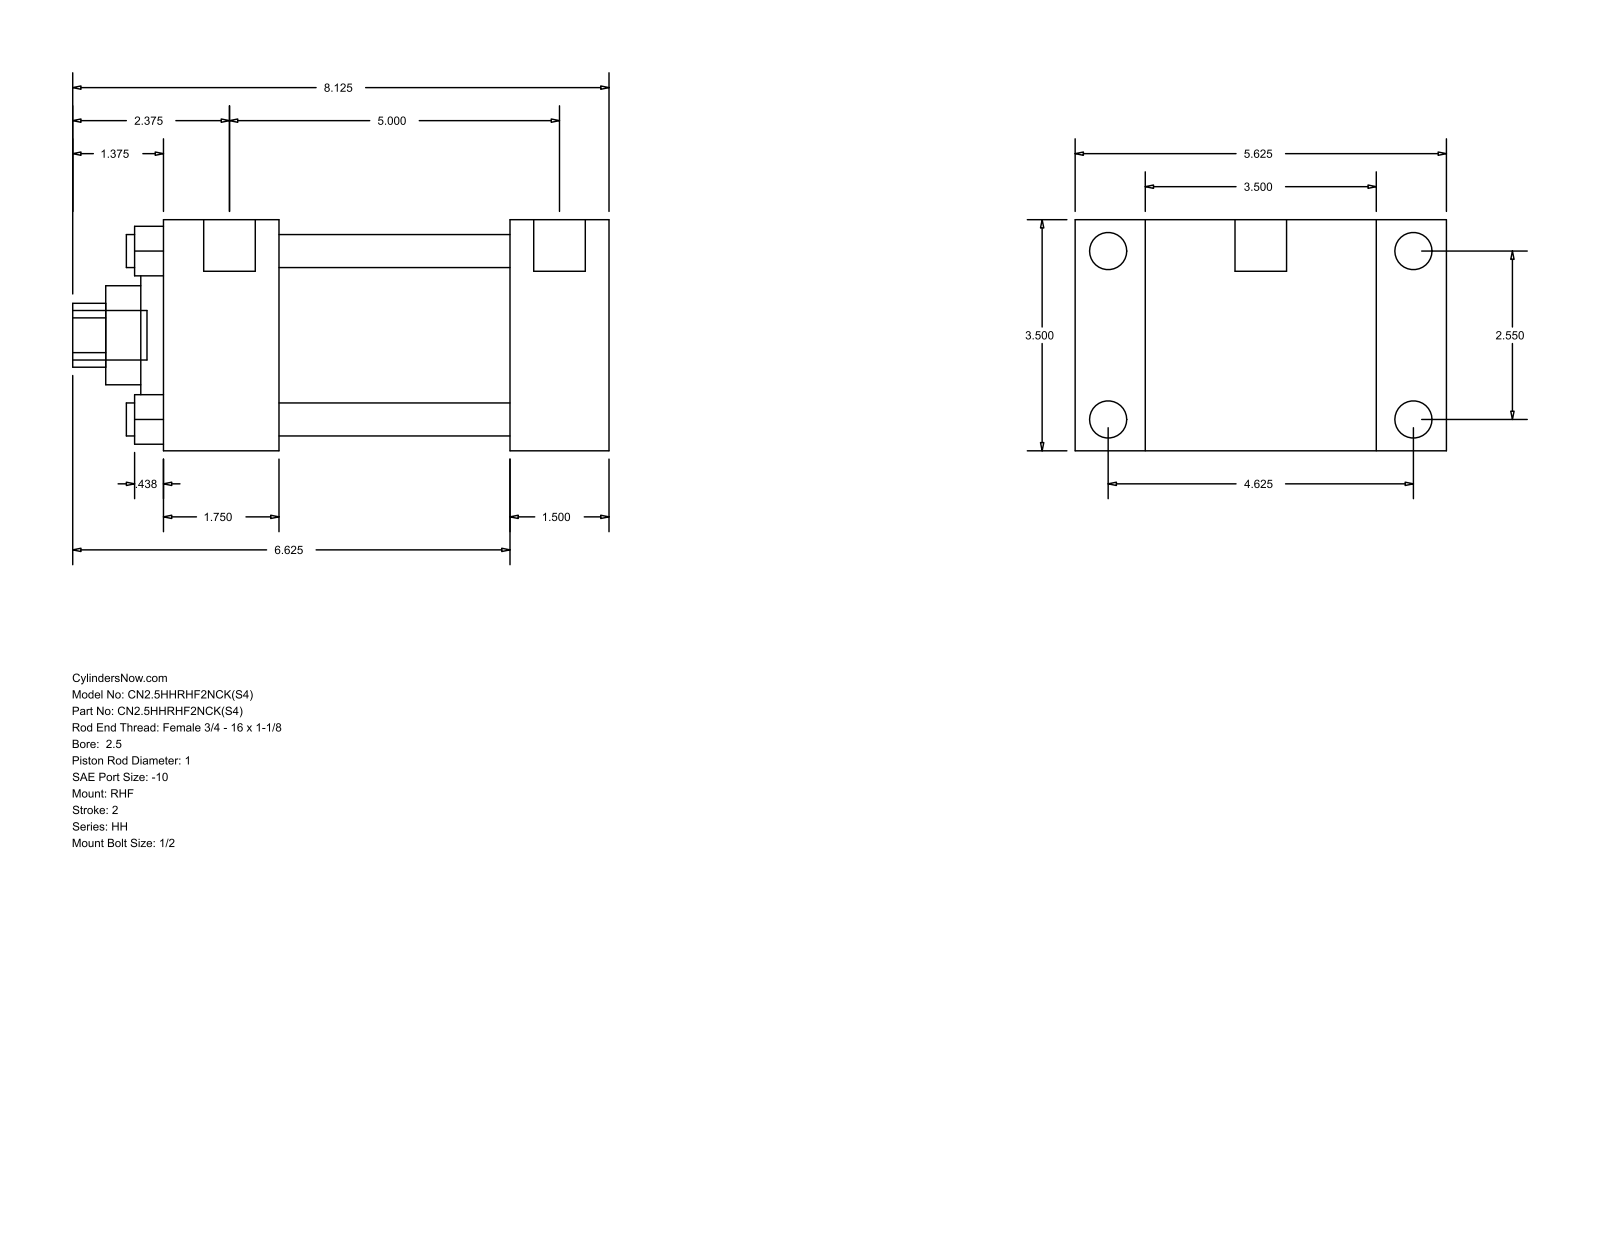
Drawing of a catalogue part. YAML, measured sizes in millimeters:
part_name: "HH_RHF__0250_1"
step_written_by: "GSSL Pune (CONFIG_CONTROL_DESIGN)"
units: millimeters
bodies: {solids: 0, faces: 90, planar: 61, cylindrical: 29, other: 0}
overall_size: [206.38, 142.88, 88.9]
round_holes:
  - {diameter: 12.7, count: 4}
  - {diameter: 25.4, count: 1}
  - {diameter: 38.1, count: 1}
  - {diameter: 60.33, count: 1}
  - {diameter: 73.03, count: 1}
round_bosses_or_shafts:
  - {diameter: 14.3, count: 4}
  - {diameter: 5.56, count: 4}
  - {diameter: 19.84, count: 2}
  - {diameter: 19.05, count: 1}
partial_cylinders:
  - {radius: 12.29, count: 1}
face_to_face_distances: [88.9, 38.1, 26.99, 115.89, 133.36, 171.46, 142.88, 44.46, 127, 8.73]
hole_center_spacings: [45.79, 64.76, 91.58]
